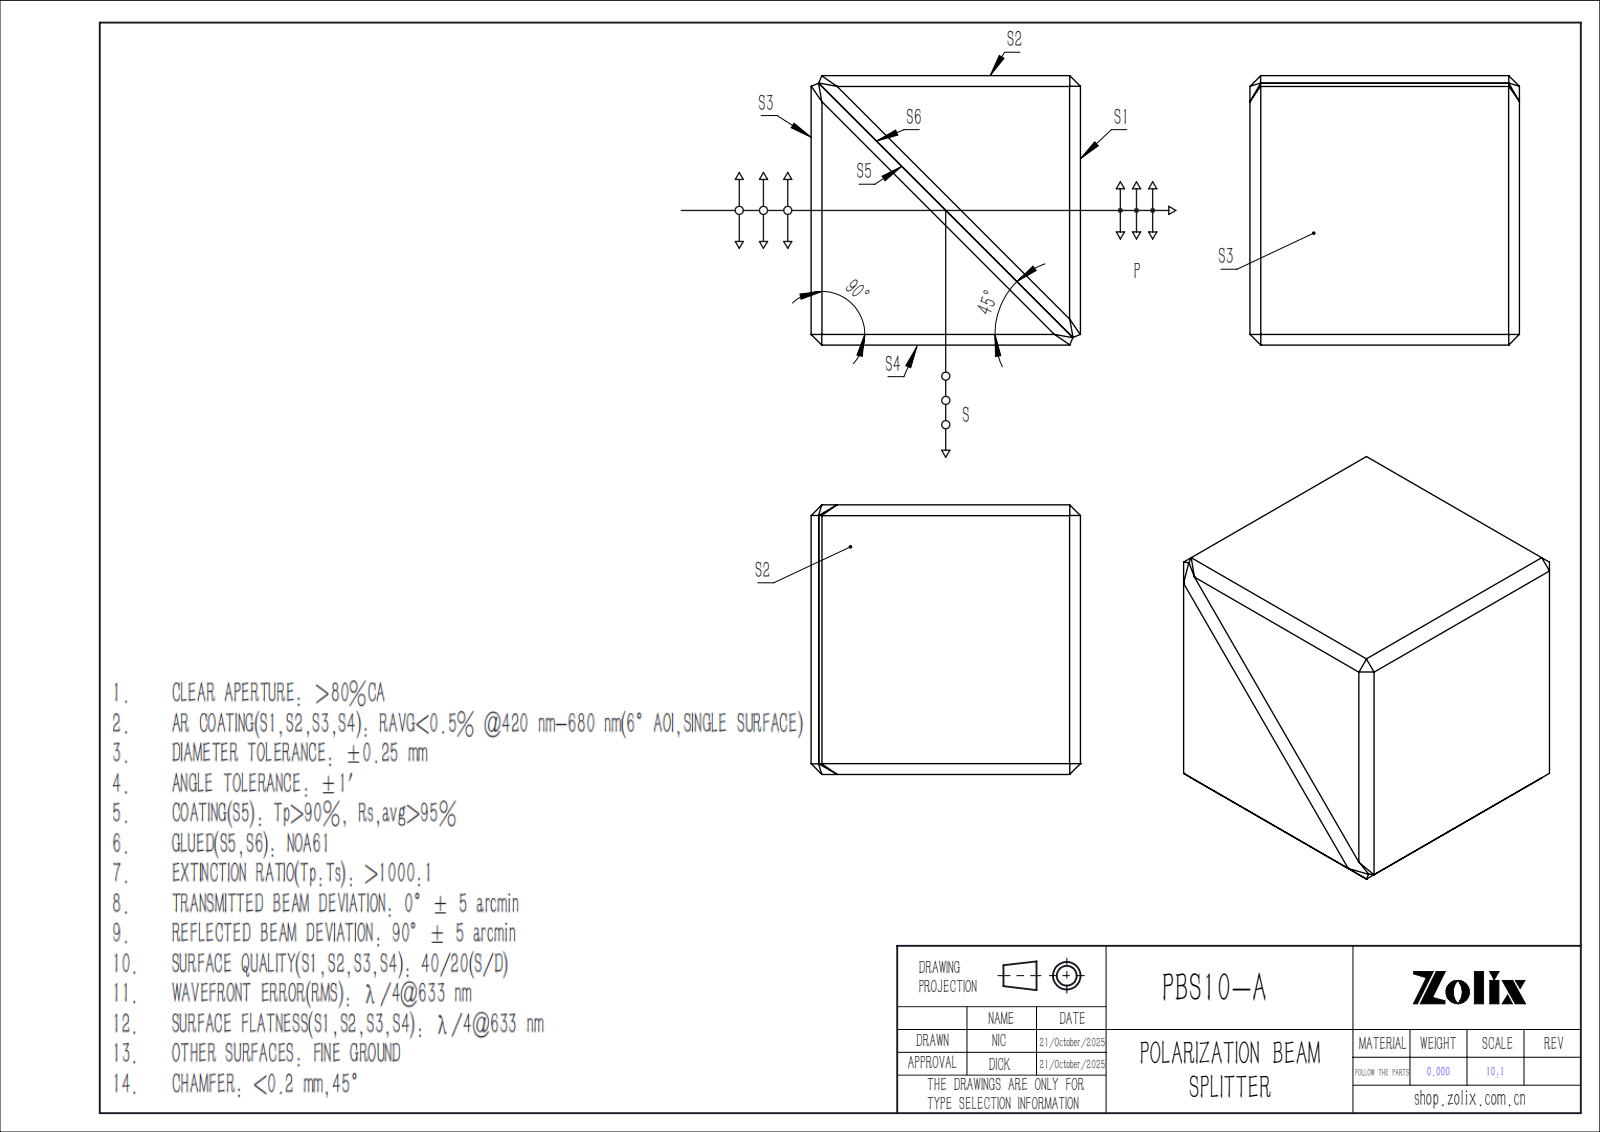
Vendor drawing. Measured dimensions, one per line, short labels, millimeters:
name: PBS611; PBS611-1-1; PBS611-1-2
written by: SolidWorks 2022 (CONFIG_CONTROL_DESIGN)
unit: mm
bodies: 2 solids, 43 faces (41 planar, 2 cylindrical, 0 other)
size: 10 × 10 × 10
volume: 996 mm³; area: 854 mm²
holes: 1× ⌀0.2
face distances: 10, 13.86, 6.79, 12.7, 6.93, 6.92, 13.85, 14.7, 16.85, 14.69
